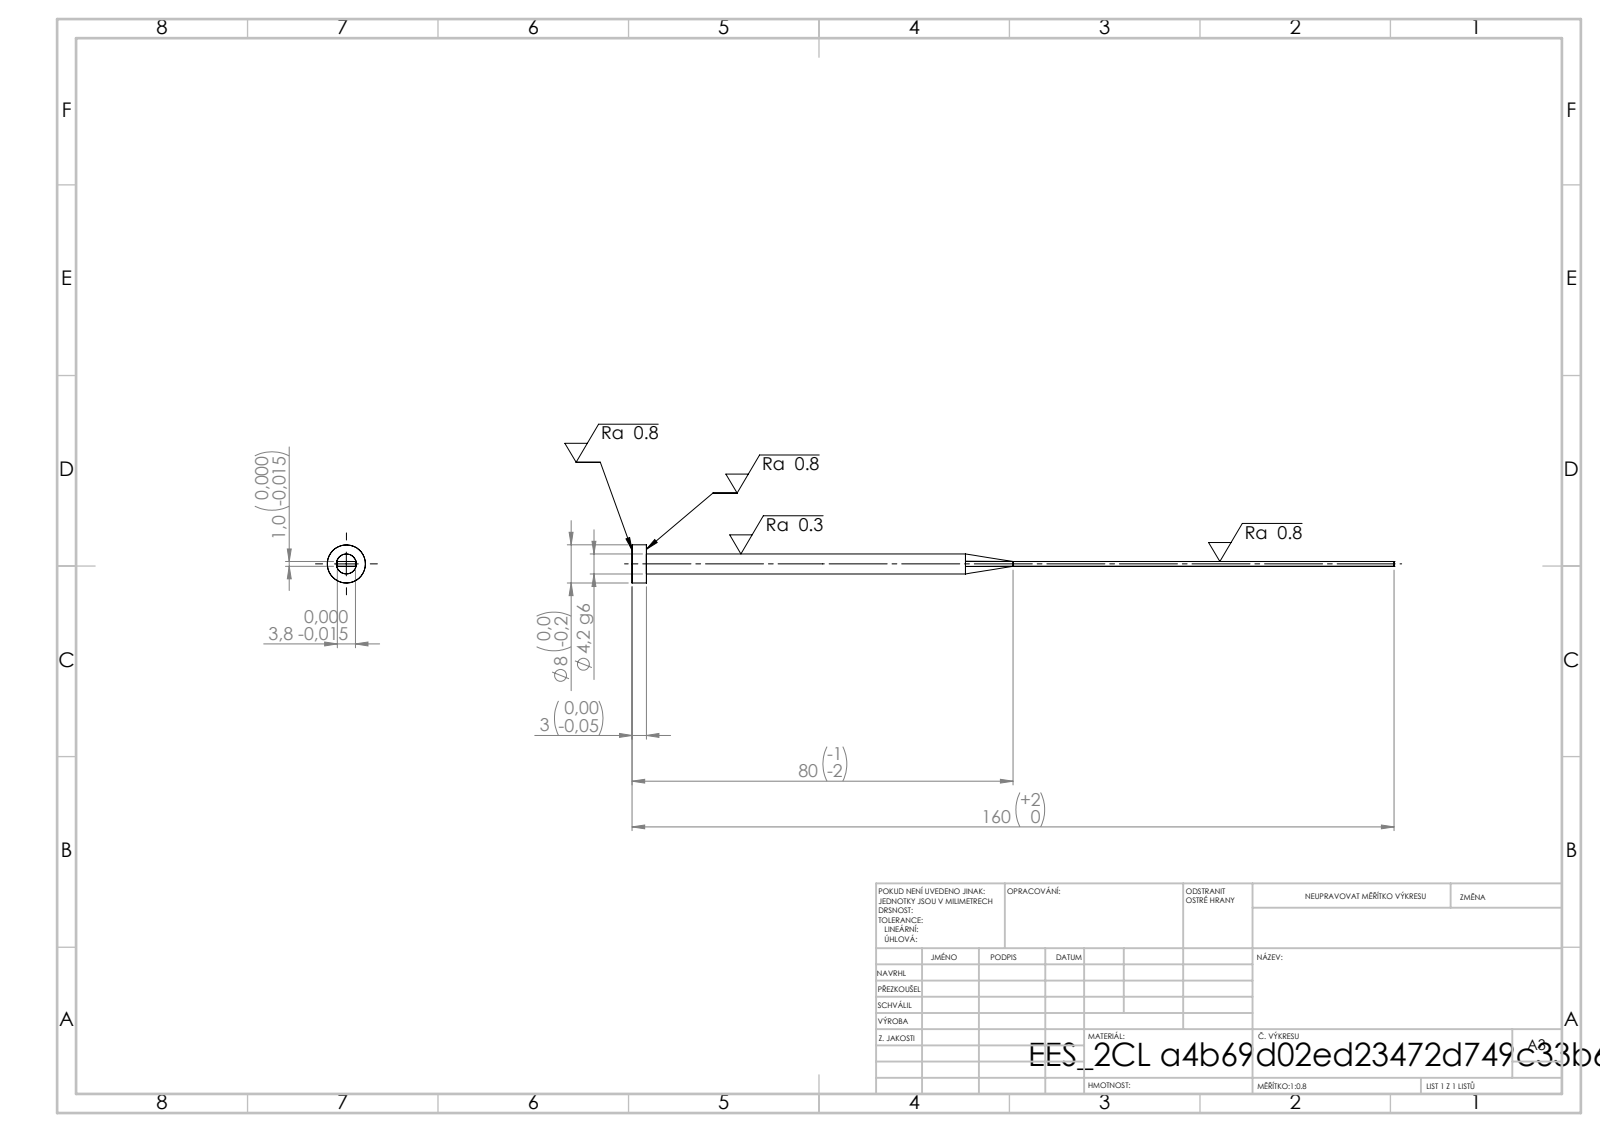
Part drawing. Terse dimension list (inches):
written by: SolidWorks 2019 (CONFIG_CONTROL_DESIGN)
unit: in
bodies: 1 solid, 15 faces (7 planar, 4 cylindrical, 4 other)
size: 6.299 × 0.315 × 0.315
volume: 0.09 in³; area: 2.988 in²
bosses: 1× ⌀0.315, 1× ⌀0.165
face distances: 0.039, 0.15, 0.118, 6.299, 6.181
